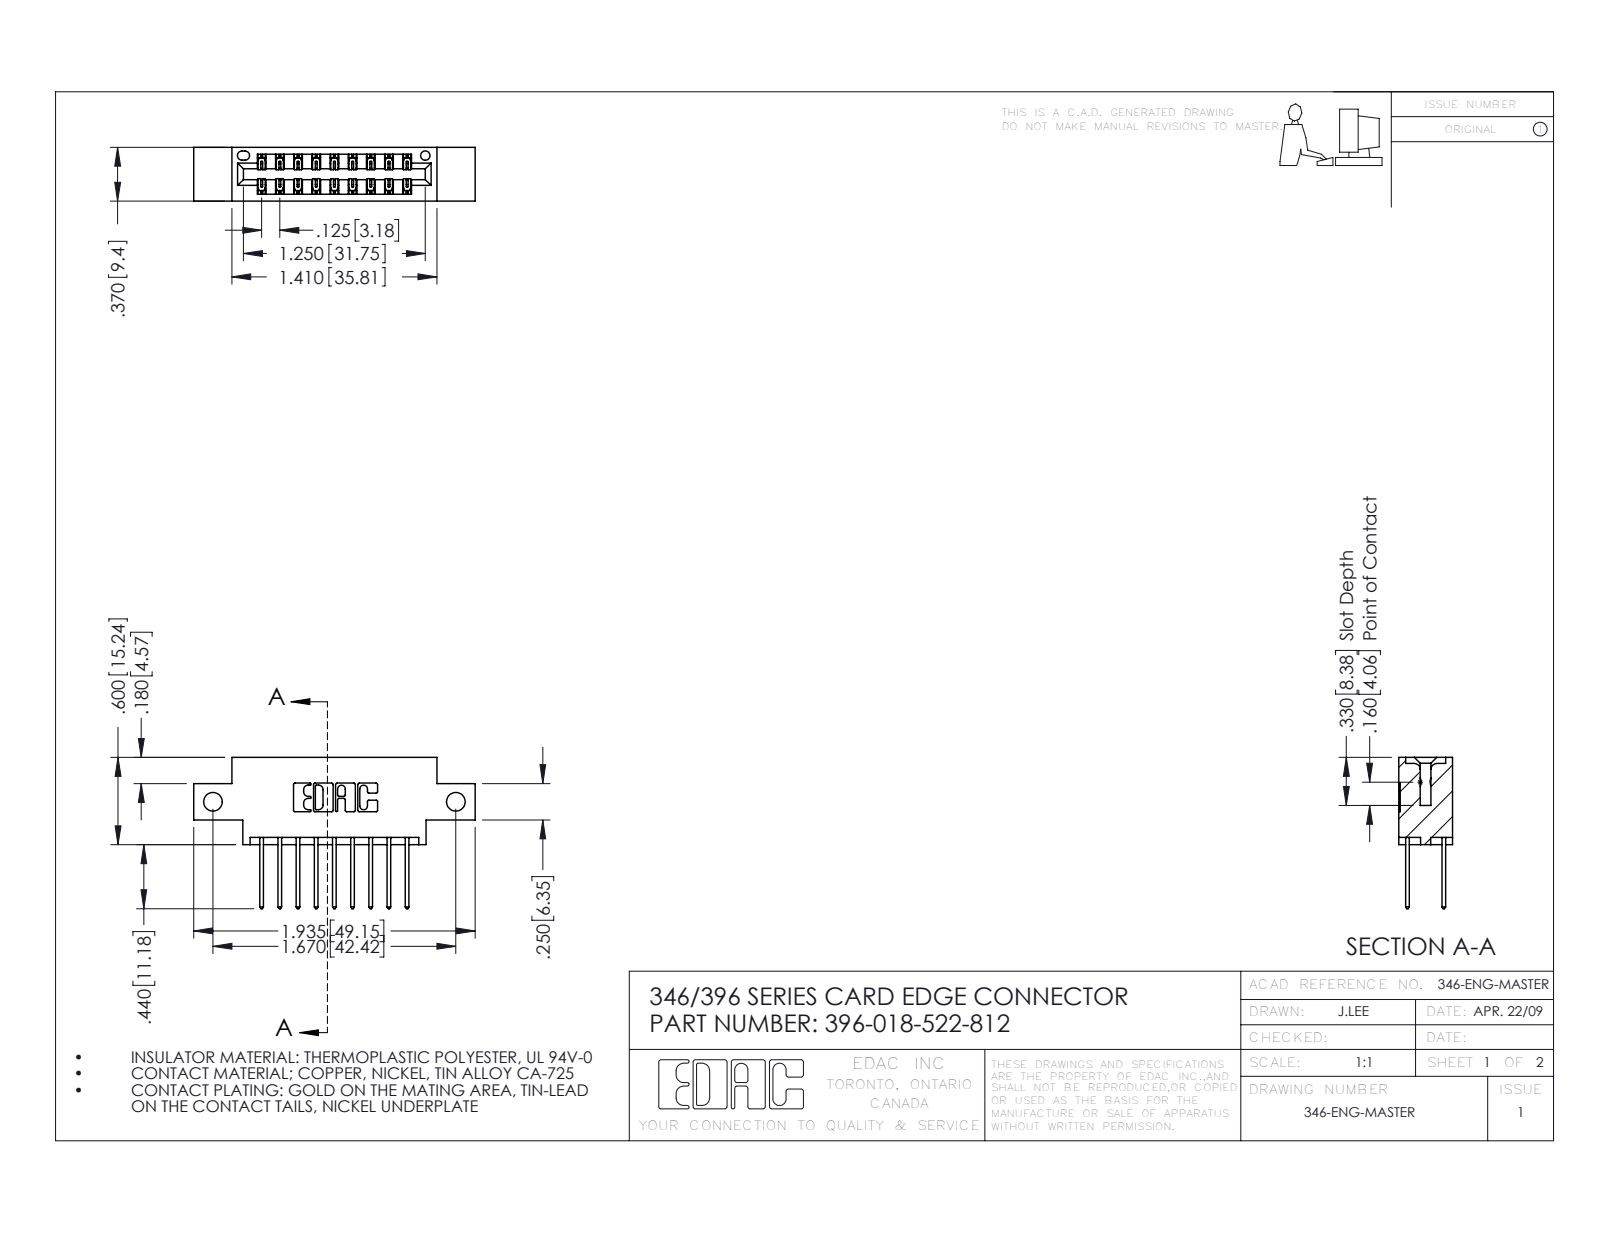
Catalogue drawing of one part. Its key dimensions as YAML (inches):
part_name: "346 Part_0.170 Offset - Side Mount; 345-292-001_345-293-122; 396-018-522-812"
step_written_by: "SolidWorks 2016 (CONFIG_CONTROL_DESIGN)"
units: inches
bodies: {solids: 19, faces: 1062, planar: 710, cylindrical: 352, other: 0}
overall_size: [1.935, 1.04, 0.37]
volume: 0.265
surface_area: 8.841
round_holes:
  - {diameter: 0.128, count: 2}
  - {diameter: 0.064, count: 1}
partial_cylinders:
  - {radius: 0.006, count: 27}
  - {radius: 0.01, count: 22}
  - {radius: 0.01, count: 18}
  - {radius: 0.007, count: 6}
  - {radius: 0.031, count: 6}
  - {radius: 0.026, count: 3}
  - {radius: 0.014, count: 2}
  - {radius: 0.022, count: 2}
face_to_face_distances: [0.25, 0.048, 0.322, 0.37, 0.072, 0.298, 0.025, 0.275, 0.148, 0.222]
hole_center_spacings: [1.67]
